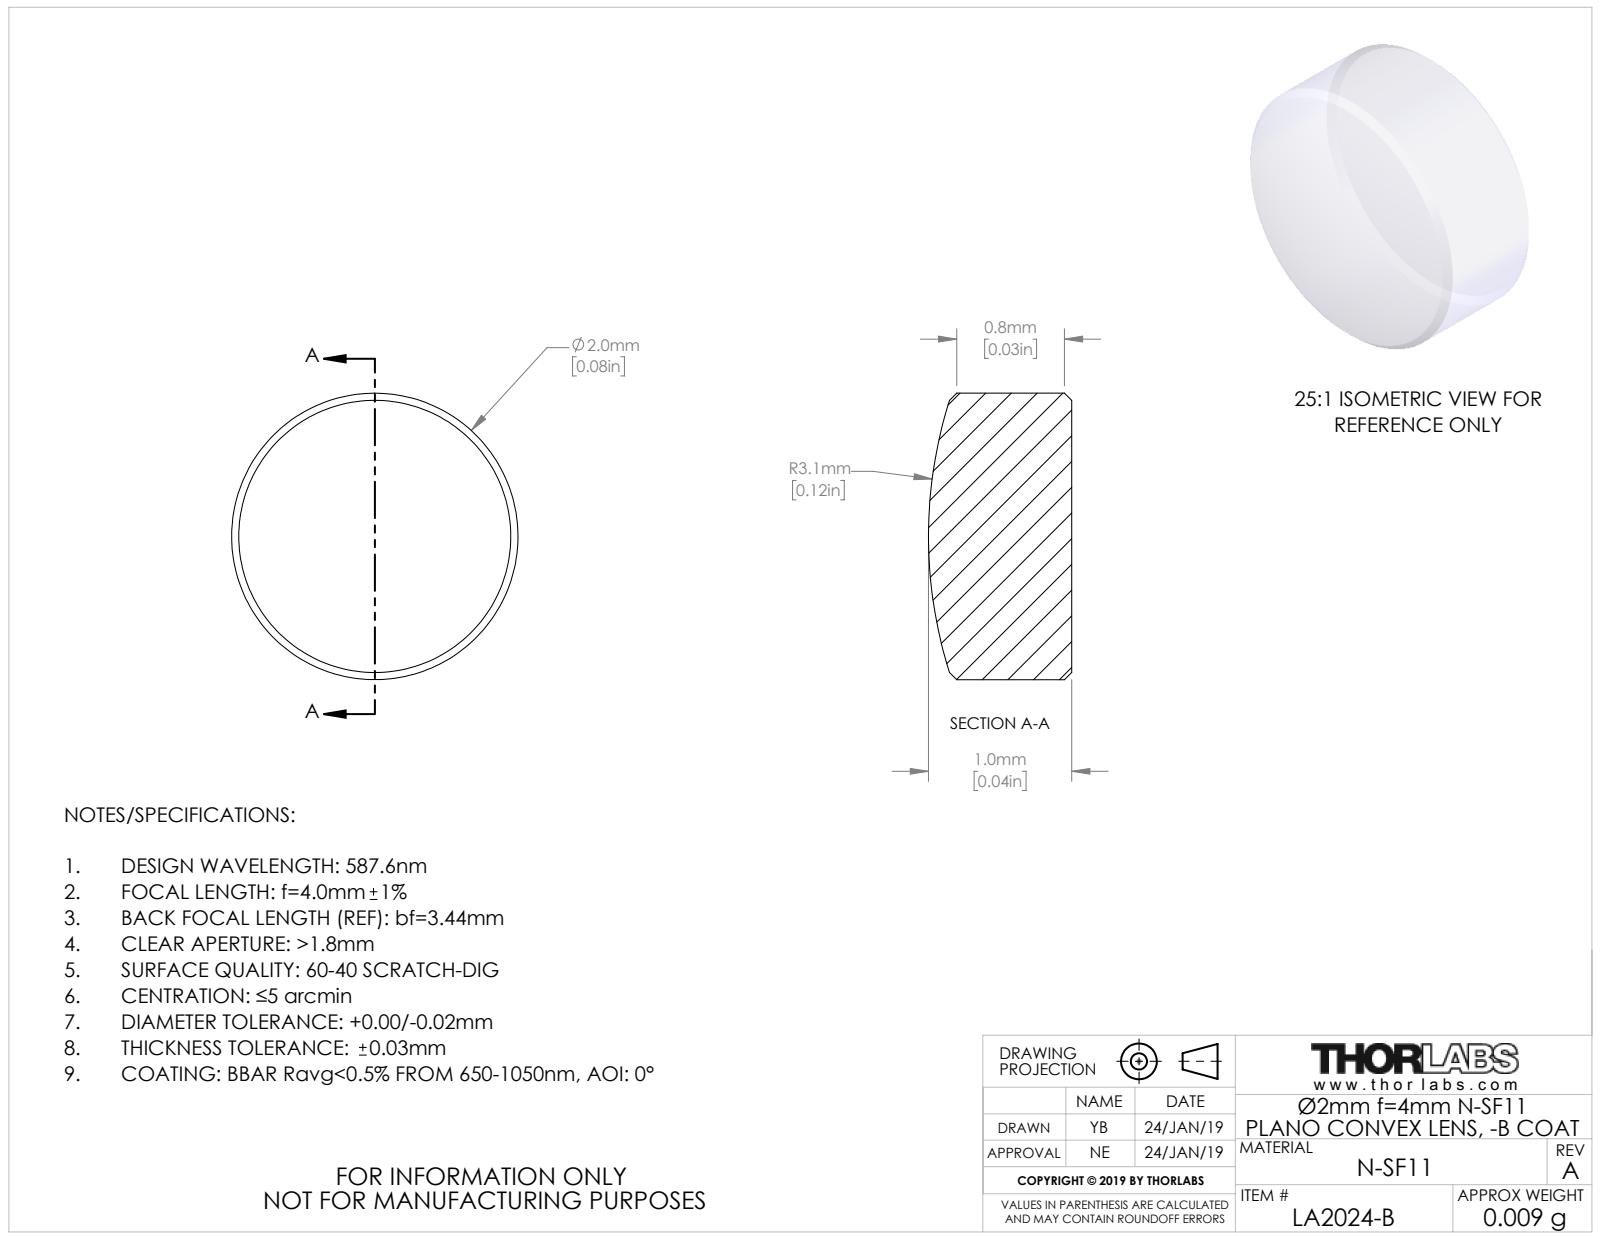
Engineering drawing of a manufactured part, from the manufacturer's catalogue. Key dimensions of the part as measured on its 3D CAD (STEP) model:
Part name (STEP PRODUCT): TTN162753-E0W
STEP written by: SolidWorks 2018 (CONFIG_CONTROL_DESIGN)
Units: millimetres
Bodies: 1 solid, 9 faces (1 planar, 2 cylindrical, 6 other)
Overall size (bounding box): 2 × 2 × 1
Volume: 3 mm³ · Surface area: 11 mm²
Round bosses / shafts (diameter × count): ⌀2 ×1
